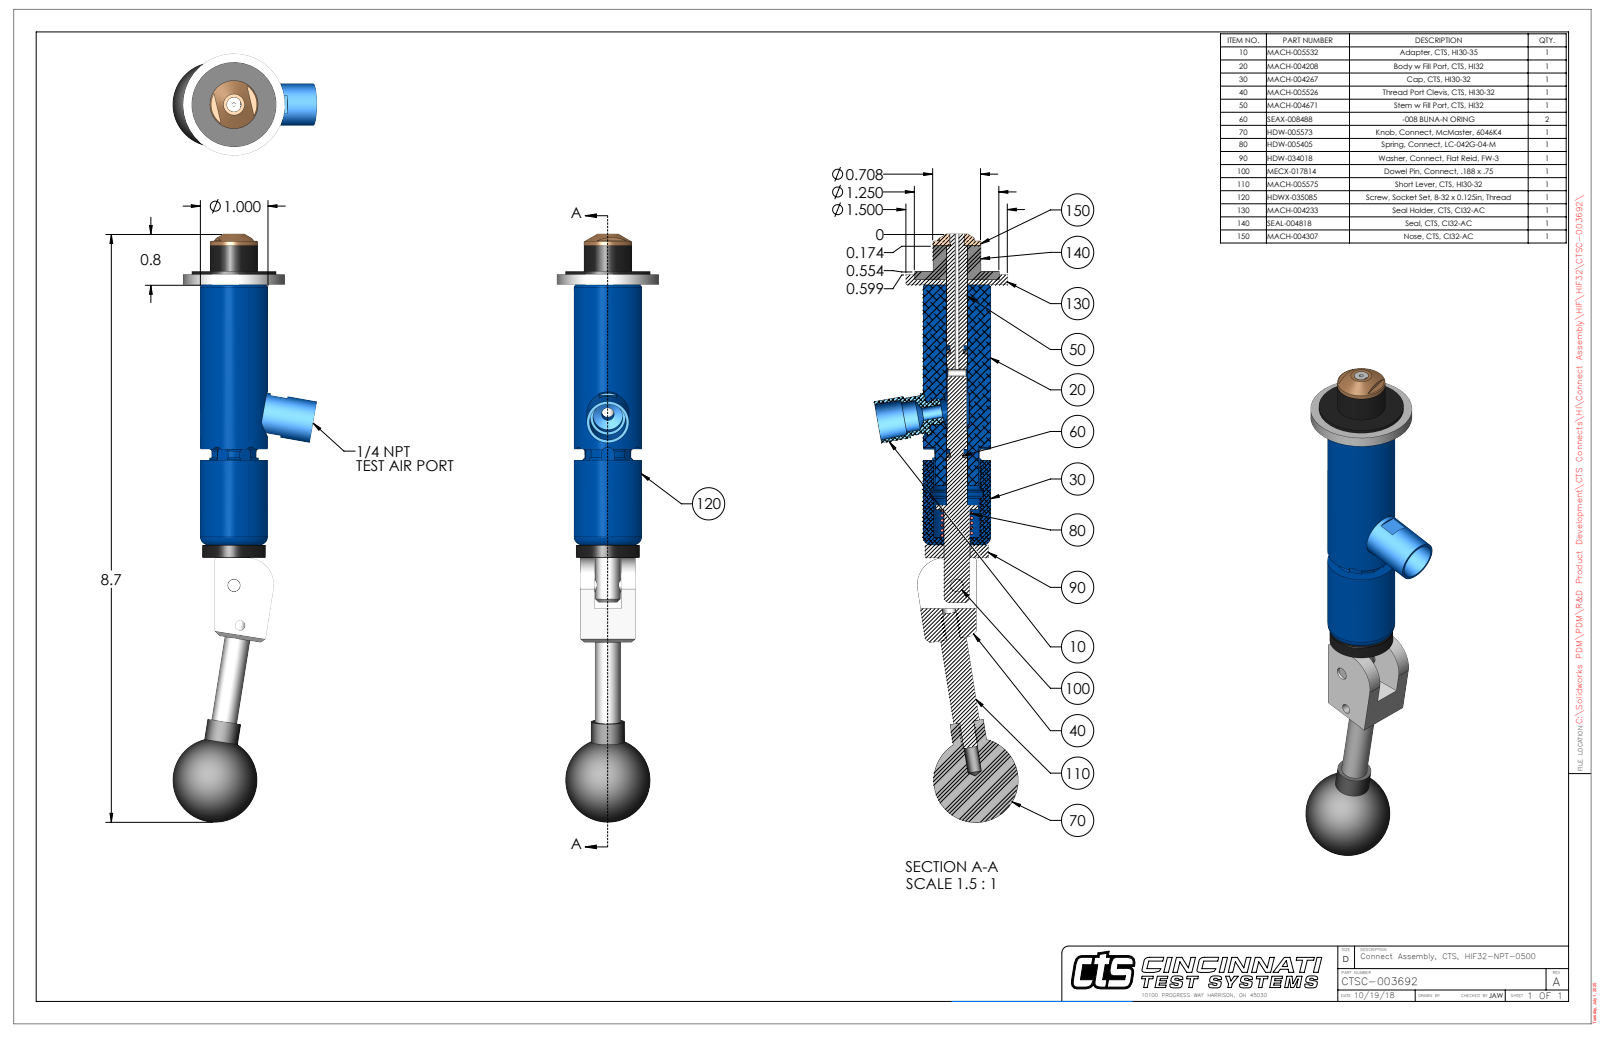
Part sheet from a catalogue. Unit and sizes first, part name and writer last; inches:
Units: inches
Overall size (bounding box): 8.692 × 2.128 × 1.5
Round holes (diameter × count): ⌀0.201 ×2, ⌀0.063 ×1, ⌀0.109 ×1, ⌀0.136 ×1, ⌀0.15 ×1, ⌀0.187 ×1, ⌀0.189 ×1, ⌀0.213 ×1, ⌀0.31 ×1, ⌀0.314 ×1, ⌀0.316 ×1, ⌀0.385 ×1
Round bosses / shafts (diameter × count): ⌀0.25 ×2, ⌀0.201 ×2, ⌀1.5 ×1, ⌀1 ×1, ⌀0.936 ×1, ⌀0.708 ×1, ⌀0.62 ×1, ⌀0.5 ×1
Partial cylindrical surfaces — rounded edges, fillets, slot ends (radius × count): R0.093 ×6, R0.029 ×2, R0.072 ×1, R0.325 ×1, R0.375 ×1, R0.4 ×1, R0.459 ×1, R0.475 ×1
Main face-to-face distances: 0.072, 0.21, 0.602, 3.916, 3.844, 0.812, 0.125, 0.197, 4.041, 0.38
Hole centre spacings: 0.599, 1.658, 2.252
Volume: 5.471 in³ · Surface area: 45.93 in²
Bodies: 9 solids, 306 faces (113 planar, 130 cylindrical, 63 other)
Part name (STEP PRODUCT): CTSC-003692
STEP written by: SolidWorks 2023 (AUTOMOTIVE_DESIGN)
